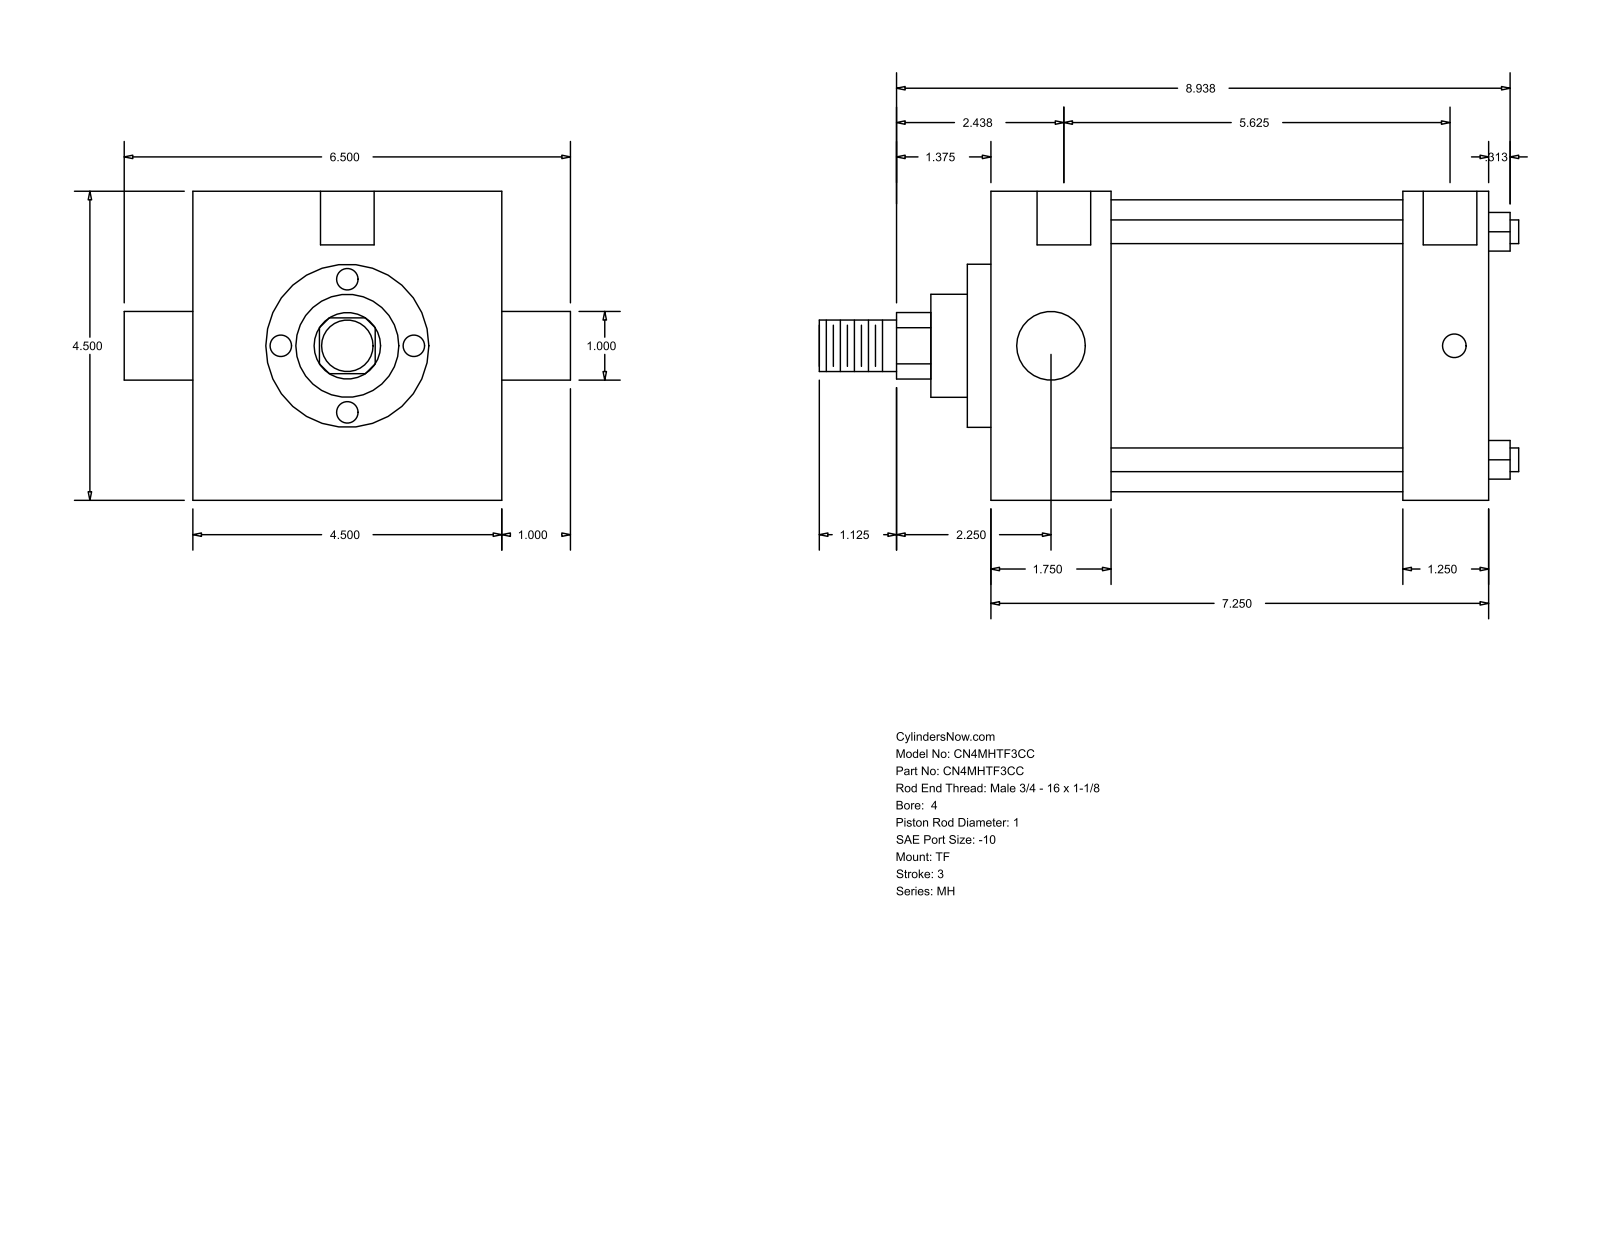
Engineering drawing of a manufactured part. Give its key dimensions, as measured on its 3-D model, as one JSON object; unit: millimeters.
{"part_name": "MH_TF__0400_1", "step_written_by": "GSSL Pune (CONFIG_CONTROL_DESIGN)", "units": "millimeters", "bodies": {"solids": 0, "faces": 86, "planar": 61, "cylindrical": 25, "other": 0}, "overall_size": [258.76, 165.1, 114.3], "round_holes": [[8.73, 3], [19.84, 2]], "round_bosses_or_shafts": [[8.76, 4], [25.4, 2], [107.95, 1], [60.33, 1], [38.1, 1], [19.05, 1]], "partial_cylinders_radius": [[12.29, 1]], "face_to_face_distances": [114.3, 184.15, 44.46, 139.69, 152.4, 107.94, 31.75, 8.73, 53.19, 161.13], "hole_center_spacings": [1.58, 1.59, 142.88, 144.46, 144.47, 146.05]}
